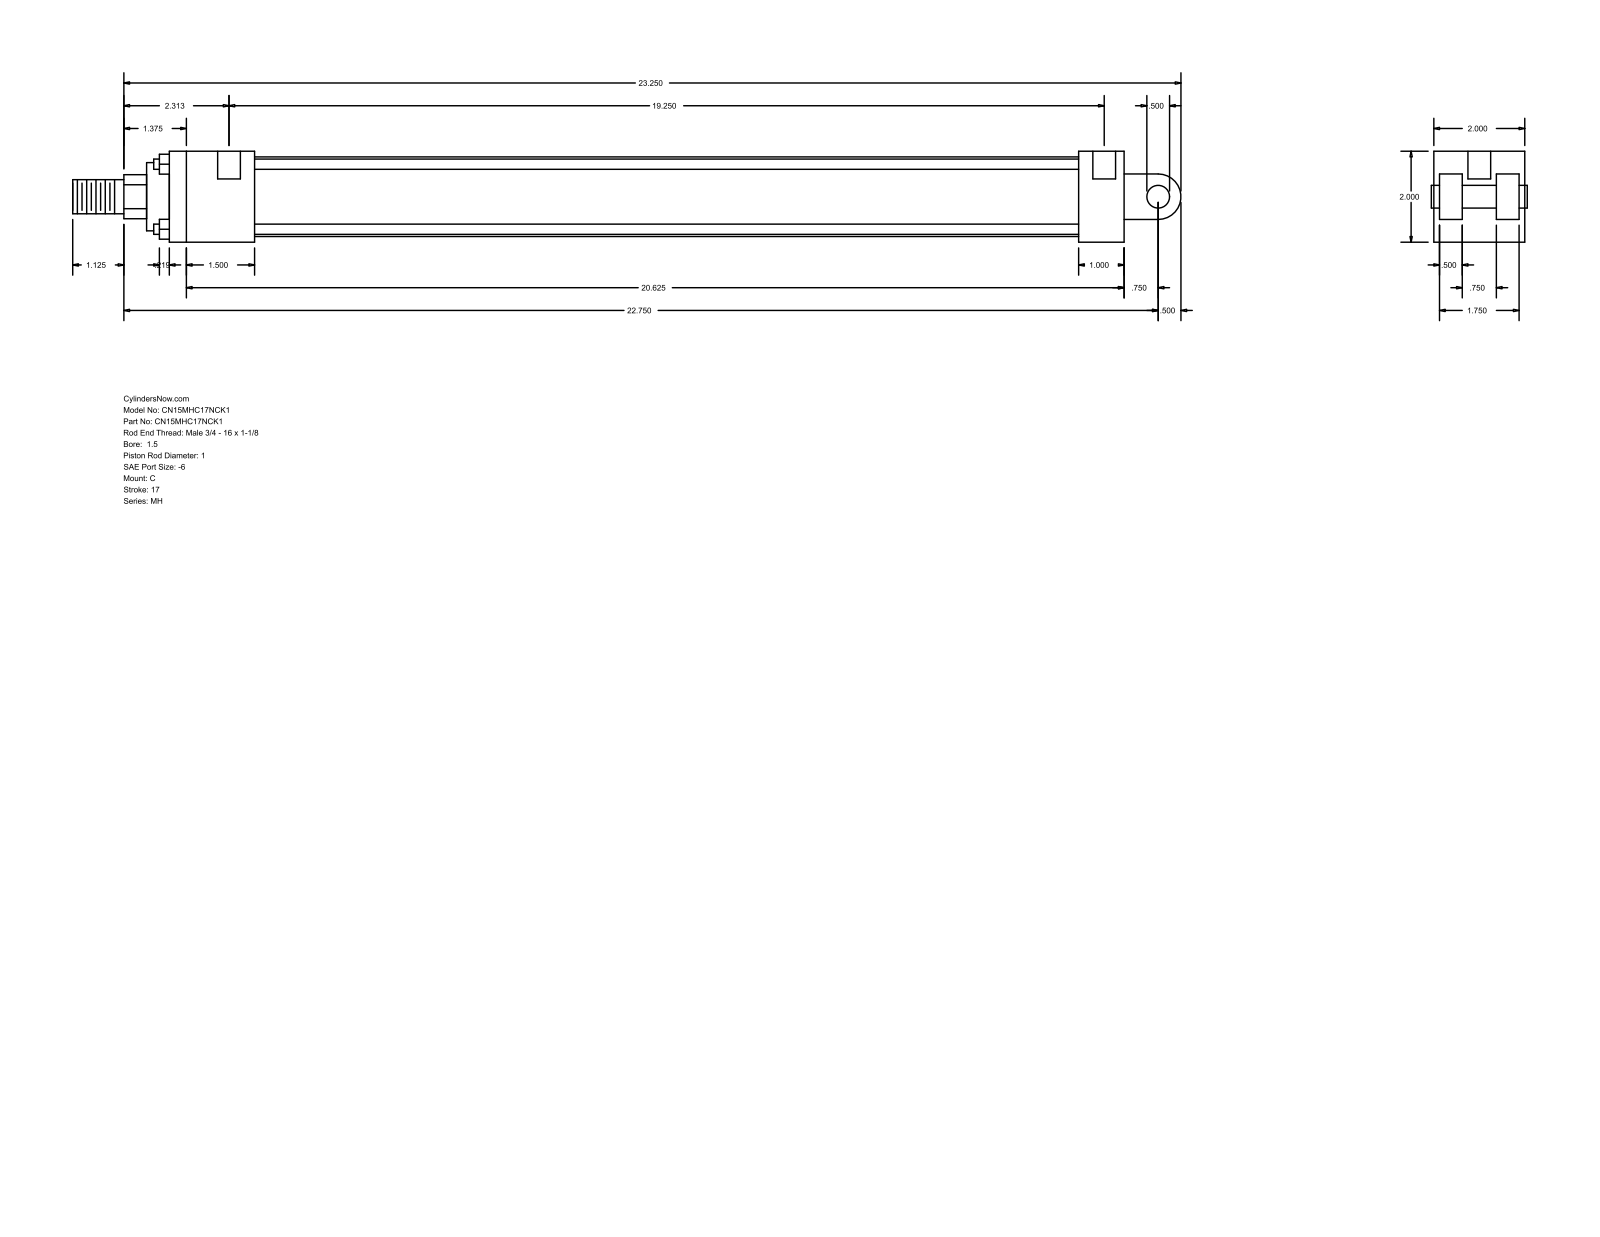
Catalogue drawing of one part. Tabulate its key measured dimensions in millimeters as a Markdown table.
| quantity | value |
| --- | --- |
| part name | MH_C__0150_1 |
| STEP written by | GSSL Pune (CONFIG_CONTROL_DESIGN) |
| units | millimeters |
| bodies | 0 solids, 99 faces (70 planar, 29 cylindrical, 0 other) |
| overall size | 619.12 × 50.8 × 50.8 |
| round holes (diameter × count) | 5.56 × 4, 12.7 × 2 |
| round bosses / shafts (diameter × count) | 5.71 × 4, 44.45 × 1, 38.1 × 1, 25.4 × 1, 19.05 × 1, 12.7 × 1 |
| partial cylindrical surfaces (radius × count) | 12.29 × 1, 12.7 × 1 |
| main face-to-face distances | 50.8, 12.7, 47.63, 25.4, 3.17, 15.87, 34.93, 31.76, 533.4, 38.1 |
| hole center spacings | 492.13, 3.18, 488.95 |
